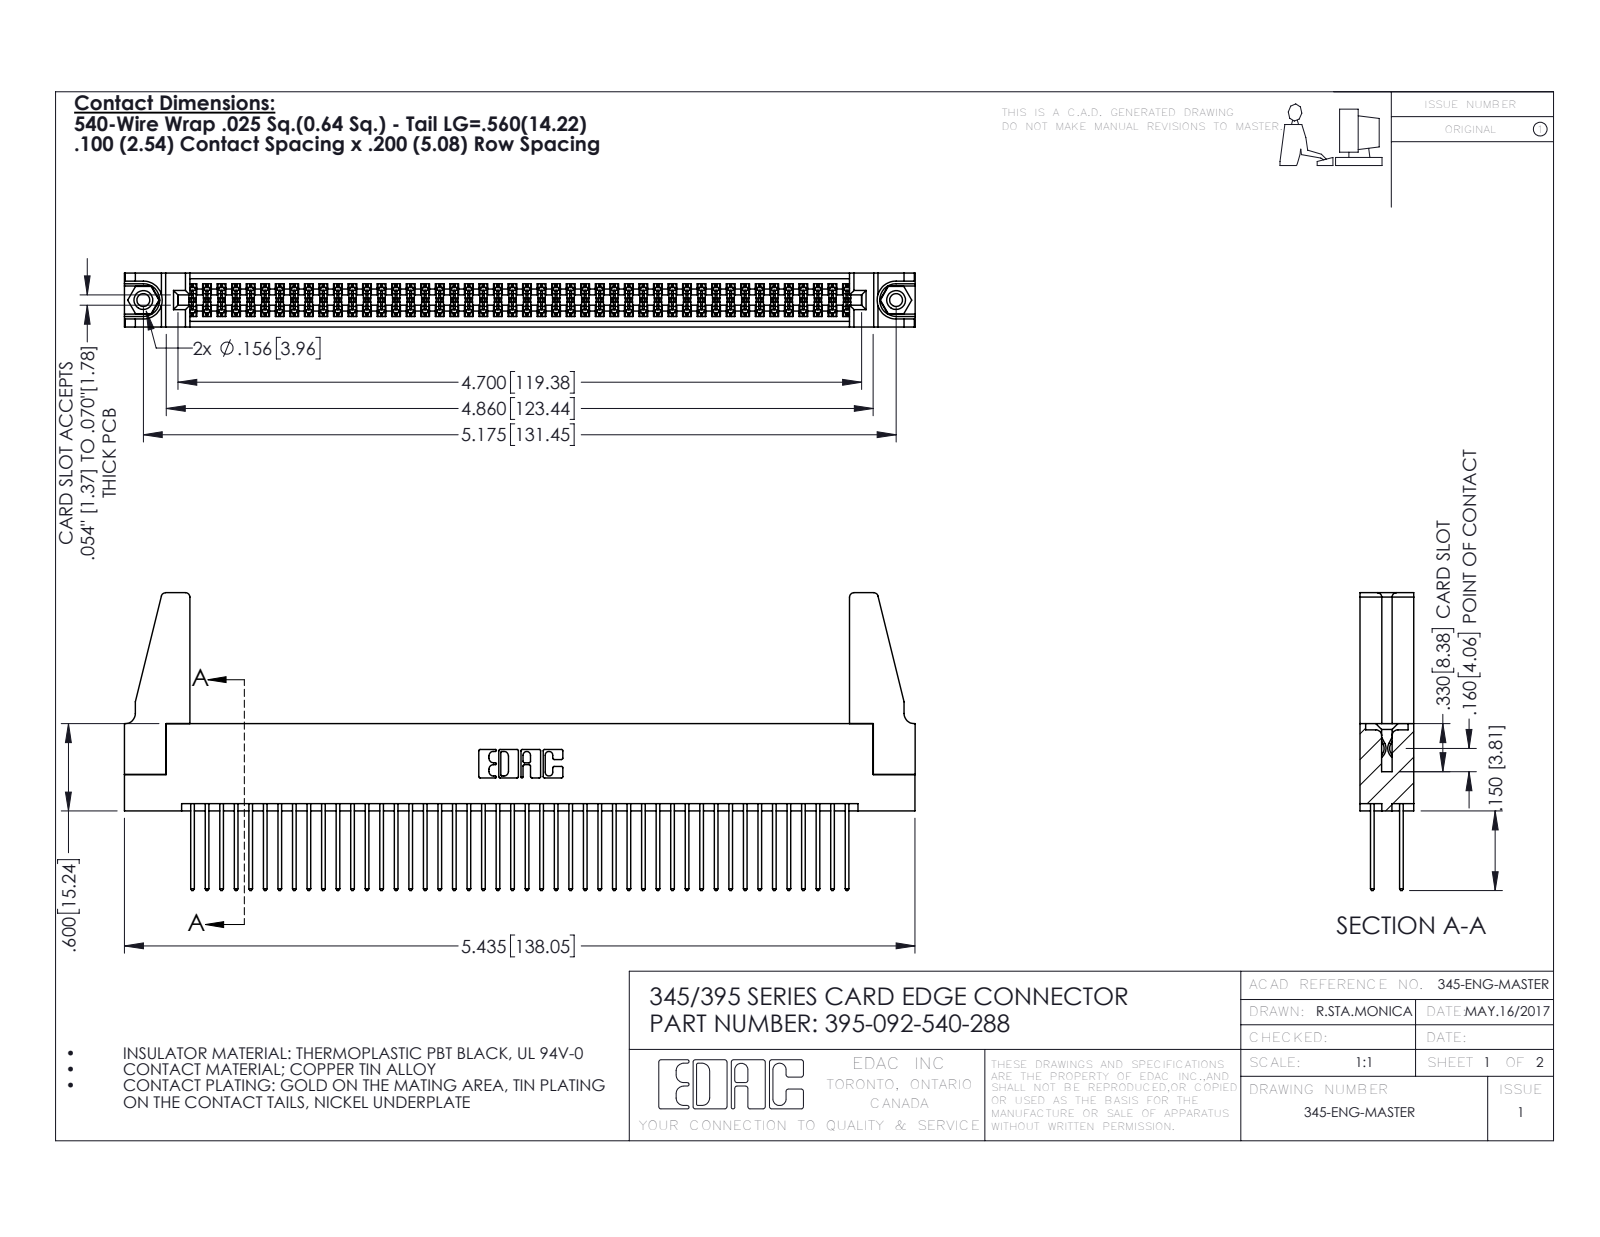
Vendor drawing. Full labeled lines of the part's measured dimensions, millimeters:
Part name (STEP PRODUCT): 345 Part_Flush Mounting Lugs - 0.156 Dia-TH; 345-250-001_345-250-001-102; 395-092-540-288; 345-220-078_345-220-088 (+1 more)
STEP written by: SolidWorks 2016 (CONFIG_CONTROL_DESIGN)
Units: millimetres
Bodies: 97 solids, 4850 faces (3188 planar, 1646 cylindrical, 16 other)
Overall size (bounding box): 138.1 × 52 × 9.4
Volume: 17 060 mm³ · Surface area: 25 210 mm²
Round holes (diameter × count): ⌀2.3 ×2, ⌀3.2 ×2, ⌀4 ×2, ⌀1.6 ×1
Round bosses / shafts (diameter × count): ⌀3.9 ×2
Partial cylindrical surfaces — rounded edges, fillets, slot ends (radius × count): R0.2 ×138, R0.3 ×92, R0.3 ×22, R0.8 ×8, R0.2 ×6, R0.8 ×6, R0.7 ×3, R0.4 ×2
Main face-to-face distances: 1.8, 7.6, 5.1, 2.5, 6.9, 0.6, 9.4, 5.7, 4.4, 3.8
Hole centre spacings: 6.9, 125.5, 131.4
